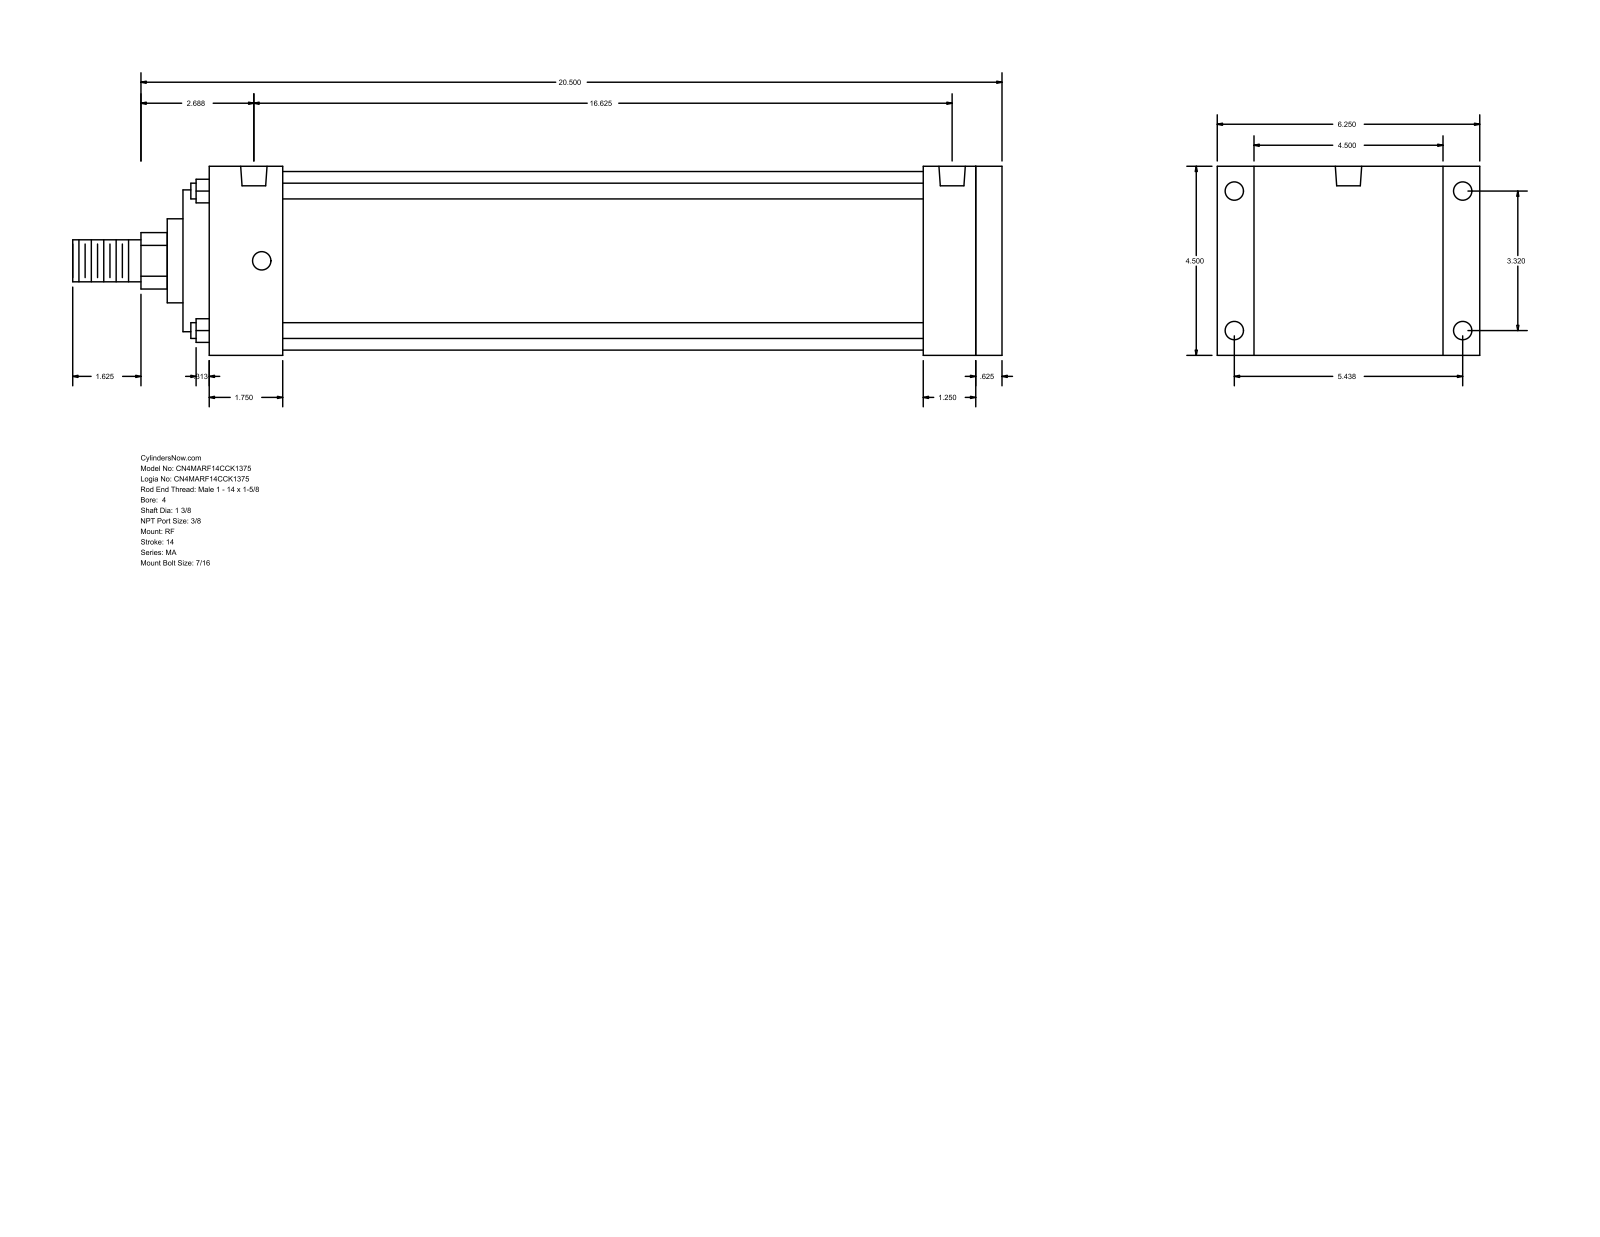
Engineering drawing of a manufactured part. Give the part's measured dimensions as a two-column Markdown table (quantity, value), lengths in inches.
| quantity | value |
| --- | --- |
| part name | MA_RF__0400_1.375 |
| STEP written by | GSSL Pune (CONFIG_CONTROL_DESIGN) |
| units | inches |
| bodies | 0 solids, 94 faces (65 planar, 29 cylindrical, 0 other) |
| overall size | 22.125 × 6.25 × 4.5 |
| round holes (diameter × count) | 0.437 × 8, 0.627 × 2 |
| round bosses / shafts (diameter × count) | 0.375 × 4, 4.25 × 1, 3.375 × 1, 2 × 1, 1.375 × 1, 1 × 1 |
| partial cylindrical surfaces (radius × count) | 0.672 × 1 |
| main face-to-face distances | 4.5, 18.875, 0.625, 18.25, 0.625, 18.875, 19.5, 0.875, 5.375, 17.625 |
| hole center spacings | 0.188, 3.32, 5.438, 6.371, 16.25, 16.437, 16.625 |
